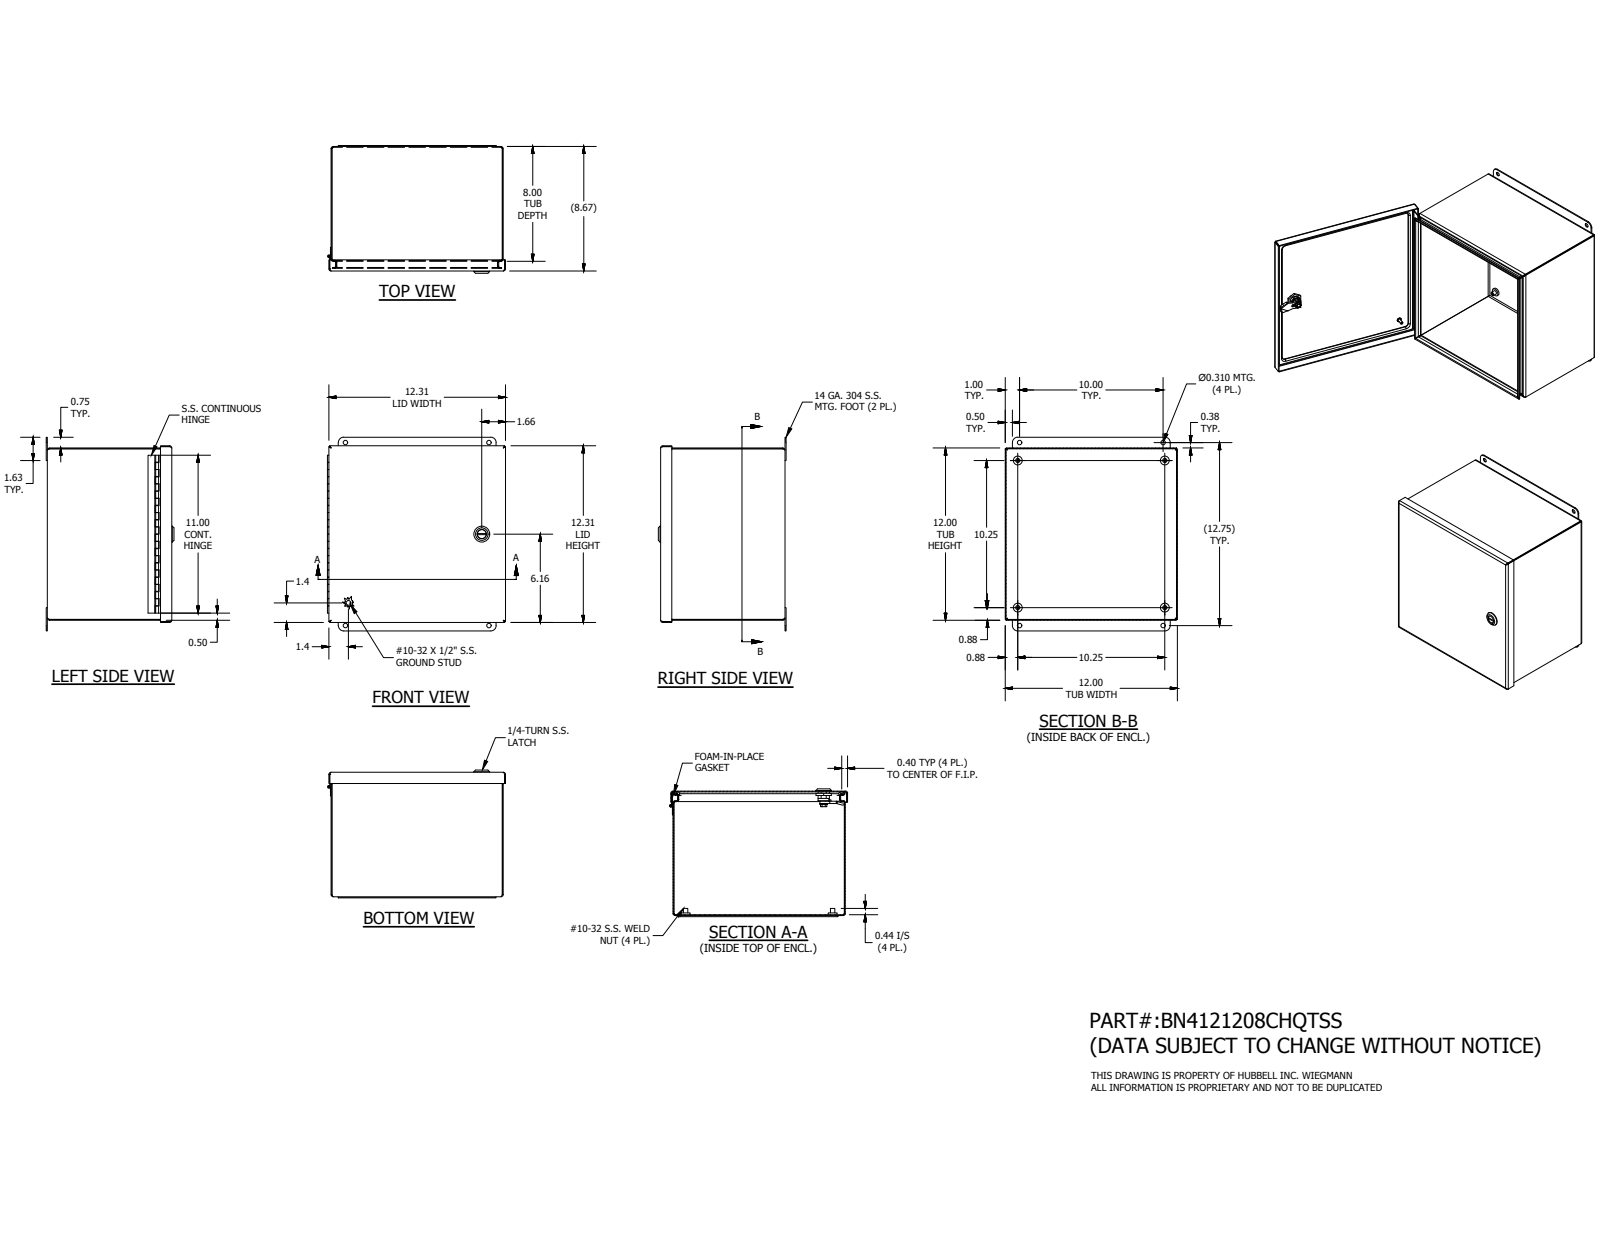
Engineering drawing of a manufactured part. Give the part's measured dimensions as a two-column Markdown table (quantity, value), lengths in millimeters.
| quantity | value |
| --- | --- |
| part name | BN41212CHQTSSLID; 12x12; 34856; H4050551LH (+8 more) |
| STEP written by | Autodesk Inventor 2016 (AUTOMOTIVE_DESIGN) |
| units | millimeters |
| bodies | 19 solids, 628 faces (335 planar, 199 cylindrical, 94 other) |
| overall size | 342.9 × 315.26 × 226.19 |
| volume | 858 963 mm³ |
| surface area | 1 086 000 mm² |
| round holes (diameter × count) | 3.96 × 4, 7.87 × 4, 2.96 × 1, 5 × 1, 8 × 1, 10 × 1, 10.2 × 1, 16.1 × 1 |
| round bosses / shafts (diameter × count) | 15.88 × 4, 7.62 × 4, 28 × 1, 19.8 × 1, 16 × 1, 15.2 × 1, 13.5 × 1, 12.8 × 1 |
| partial cylindrical surfaces (radius × count) | 2.38 × 20, 3.88 × 20, 3.17 × 16, 0.5 × 8, 4 × 4, 9.53 × 4, 2.31 × 2, 6.45 × 1 |
| main face-to-face distances | 1.5, 303.3, 1.49, 304.8, 218.79, 220.28, 217.29, 218.78, 303.31, 301.81 |
| hole center spacings | 31.91, 260.35, 292.12, 389.18, 131.14, 254, 259.12, 259.13 |
